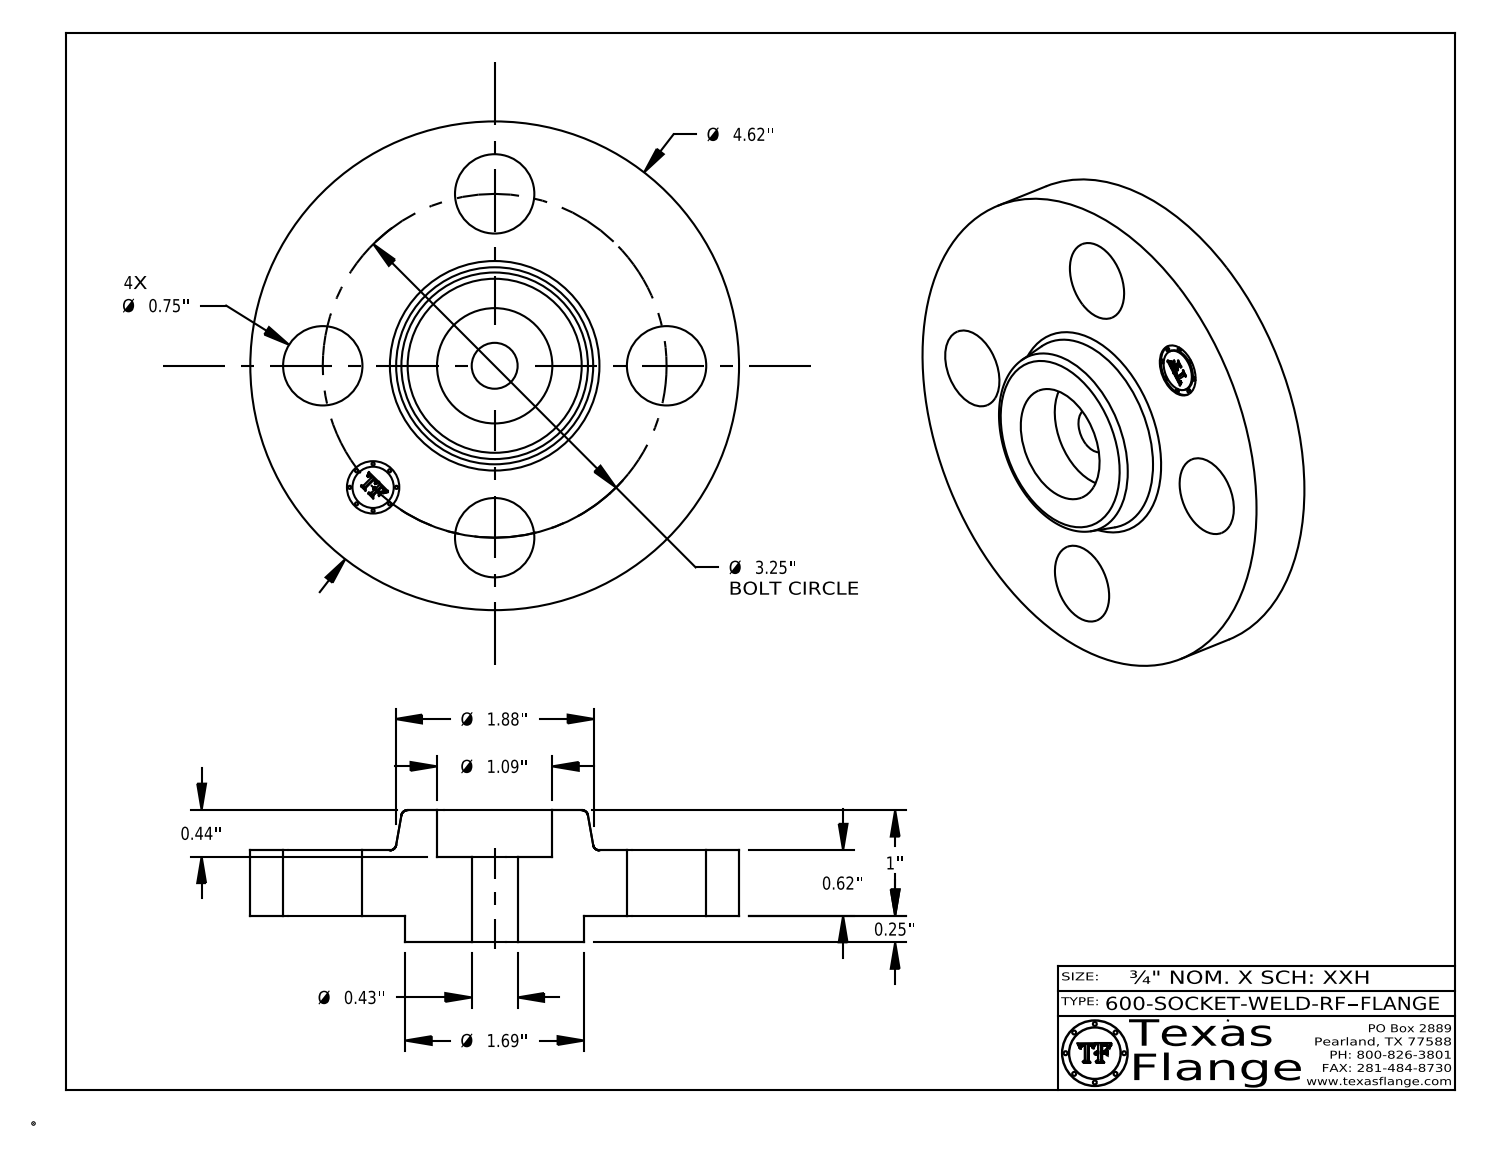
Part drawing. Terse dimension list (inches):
name: 600-SOCKET-WELD-RF
written by: CATIA V5 STEP AP214 (AUTOMOTIVE_DESIGN)
unit: in
bodies: 1 solid, 412 faces (370 planar, 36 cylindrical, 6 other)
size: 4.62 × 4.62 × 1.25
volume: 10.31 in³; area: 50.19 in²
holes: 4× ⌀0.75, 1× ⌀0.434, 1× ⌀0.495, 1× ⌀1.09
bosses: 8× ⌀0.03, 1× ⌀4.62, 1× ⌀1.69, 1× ⌀0.39
face distances: 0.62, 0.25, 0.87, 1.25, 1, 0.38, 0.81, 0.56, 0.06, 0.44
hole spacings: 1.625, 2.298, 1.244, 3.003, 3.25
